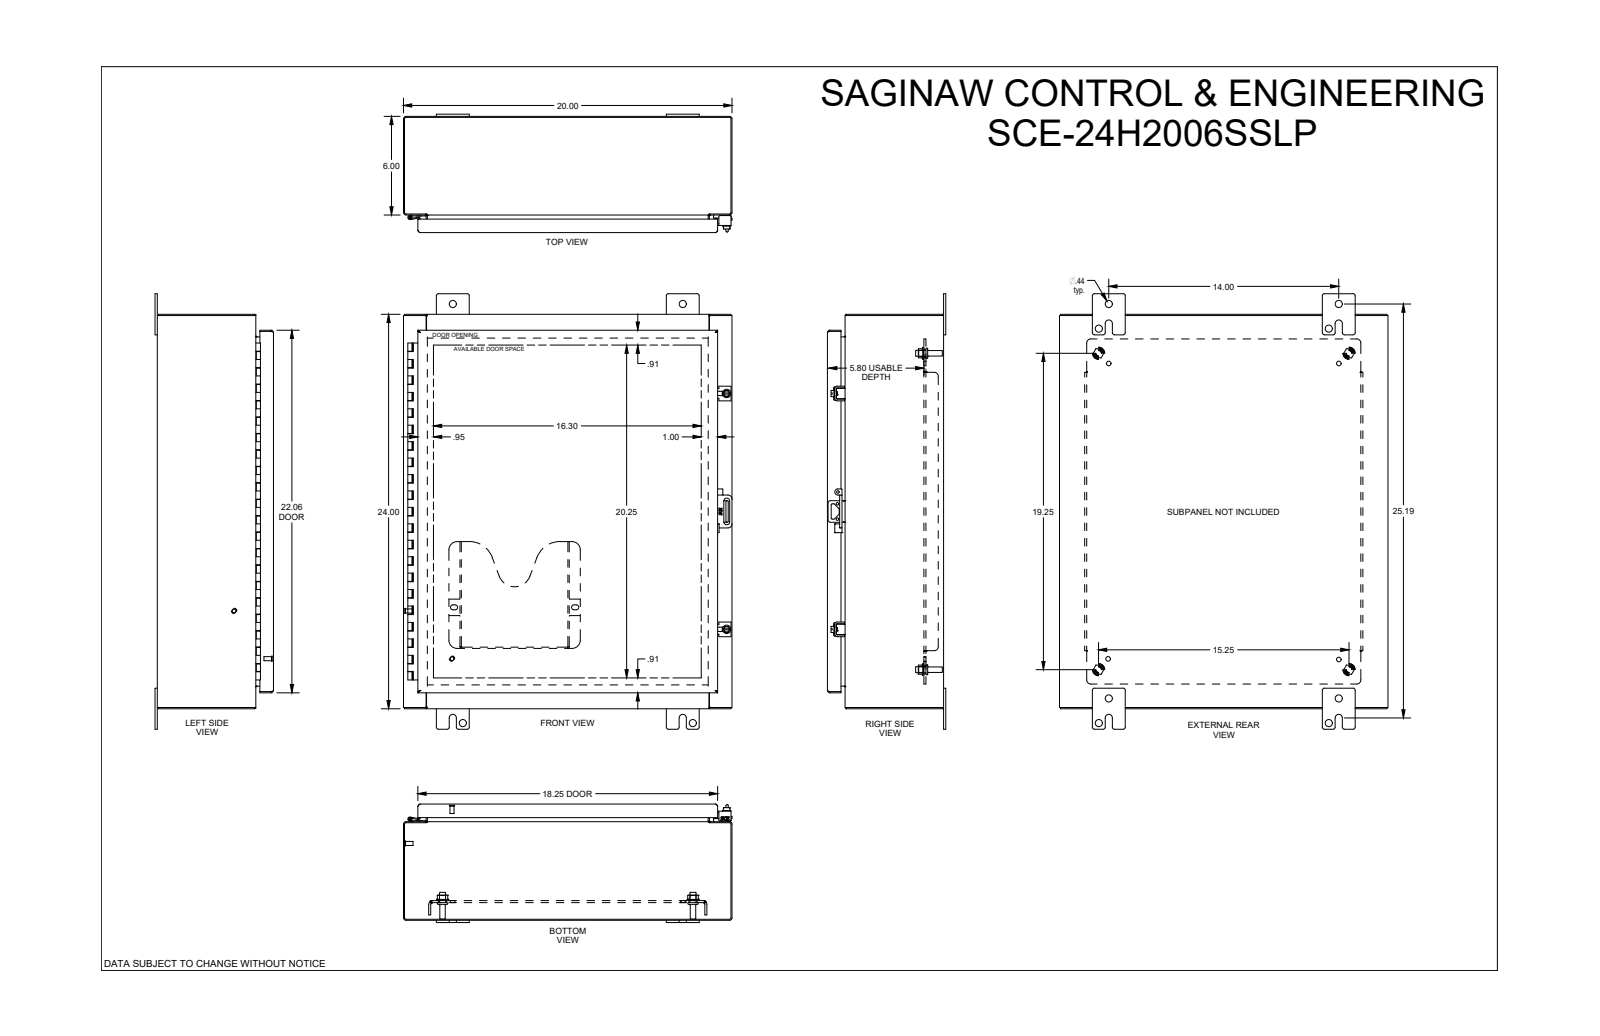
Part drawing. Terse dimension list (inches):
name: SCE-24H2006SSLP
written by: SolidWorks 2019 (CONFIG_CONTROL_DESIGN)
unit: in
bodies: 0 solids, 3160 faces (1275 planar, 660 cylindrical, 1225 other)
size: 26.5 × 20 × 7.208
holes: 8× ⌀0.437, 5× ⌀0.25, 4× ⌀0.19, 4× ⌀0.193, 4× ⌀0.281, 4× ⌀0.367, 4× ⌀0.5, 2× ⌀0.16, 2× ⌀0.203, 1× ⌀0.13, 1× ⌀0.132
bosses: 7× ⌀0.248, 5× ⌀0.563, 4× ⌀0.366, 4× ⌀0.332, 4× ⌀0.256, 4× ⌀0.188, 3× ⌀0.25, 2× ⌀0.507
rounds: 114× R0.01, 36× R0.015, 30× R0.029, 27× R0.03, 27× R0.125, 25× R0.06, 22× R0.04, 14× R0.07
face distances: 0.075, 6.998, 6.923, 0.075, 7.073, 6.998, 5.923, 1.2, 1.125, 5.798
hole spacings: 0.875, 14, 6.5, 14.644, 18.641, 23.689, 0.515, 1.439
